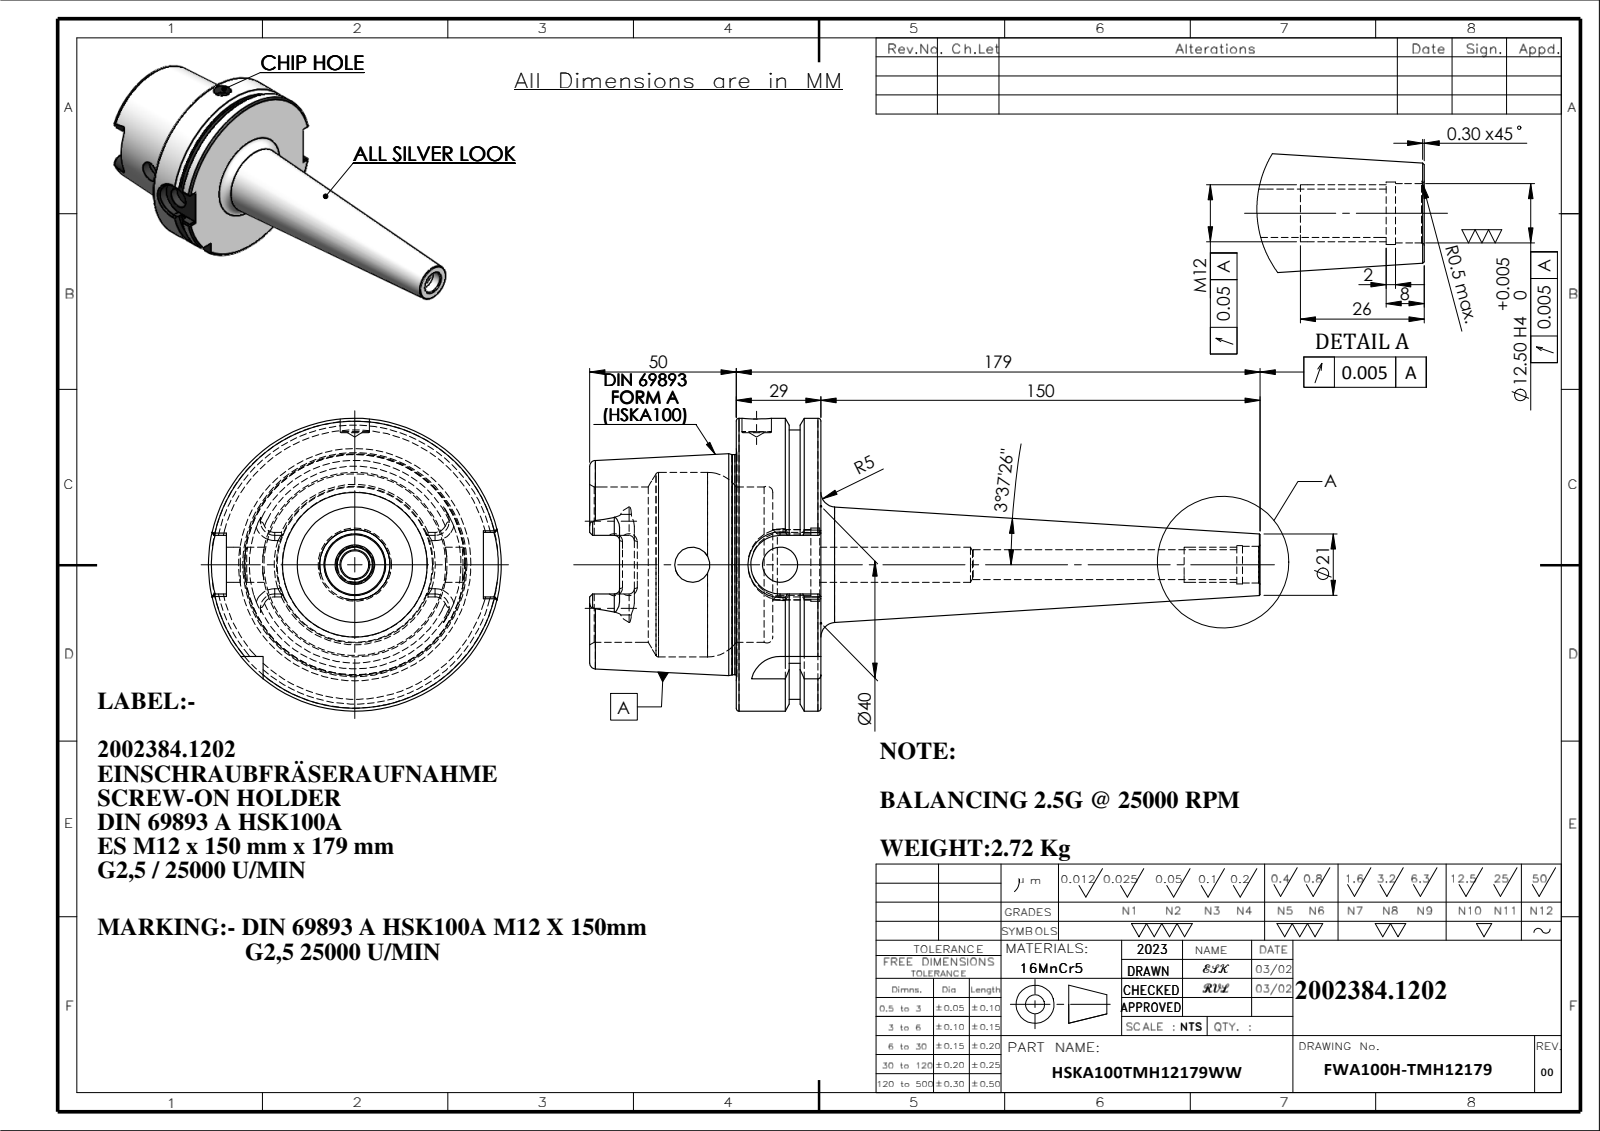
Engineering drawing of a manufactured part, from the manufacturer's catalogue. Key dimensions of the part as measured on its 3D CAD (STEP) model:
Part name (STEP PRODUCT): 91100A-ES8M12150
STEP written by: SolidWorks 2018 (CONFIG_CONTROL_DESIGN)
Units: millimetres
Bodies: 1 solid, 176 faces (50 planar, 52 cylindrical, 74 other)
Overall size (bounding box): 228.95 × 100 × 100
Volume: 353 218 mm³ · Surface area: 68 136 mm²
Round holes (diameter × count): ⌀12 ×3, ⌀10 ×1, ⌀10.2 ×1, ⌀12.5 ×1, ⌀13.1 ×1, ⌀21 ×1, ⌀25 ×1, ⌀53 ×1, ⌀63 ×1
Round bosses / shafts (diameter × count): ⌀100 ×1, ⌀92 ×1, ⌀75.16 ×1
Partial cylindrical surfaces — rounded edges, fillets, slot ends (radius × count): R1.8 ×6, R4.88 ×4, R10 ×2, R11 ×1
Main face-to-face distances: 28.95, 12.5, 16.45, 50, 62.5, 78.95, 71.87, 21.87, 9.37, 7.08
Hole centre spacings: 30
